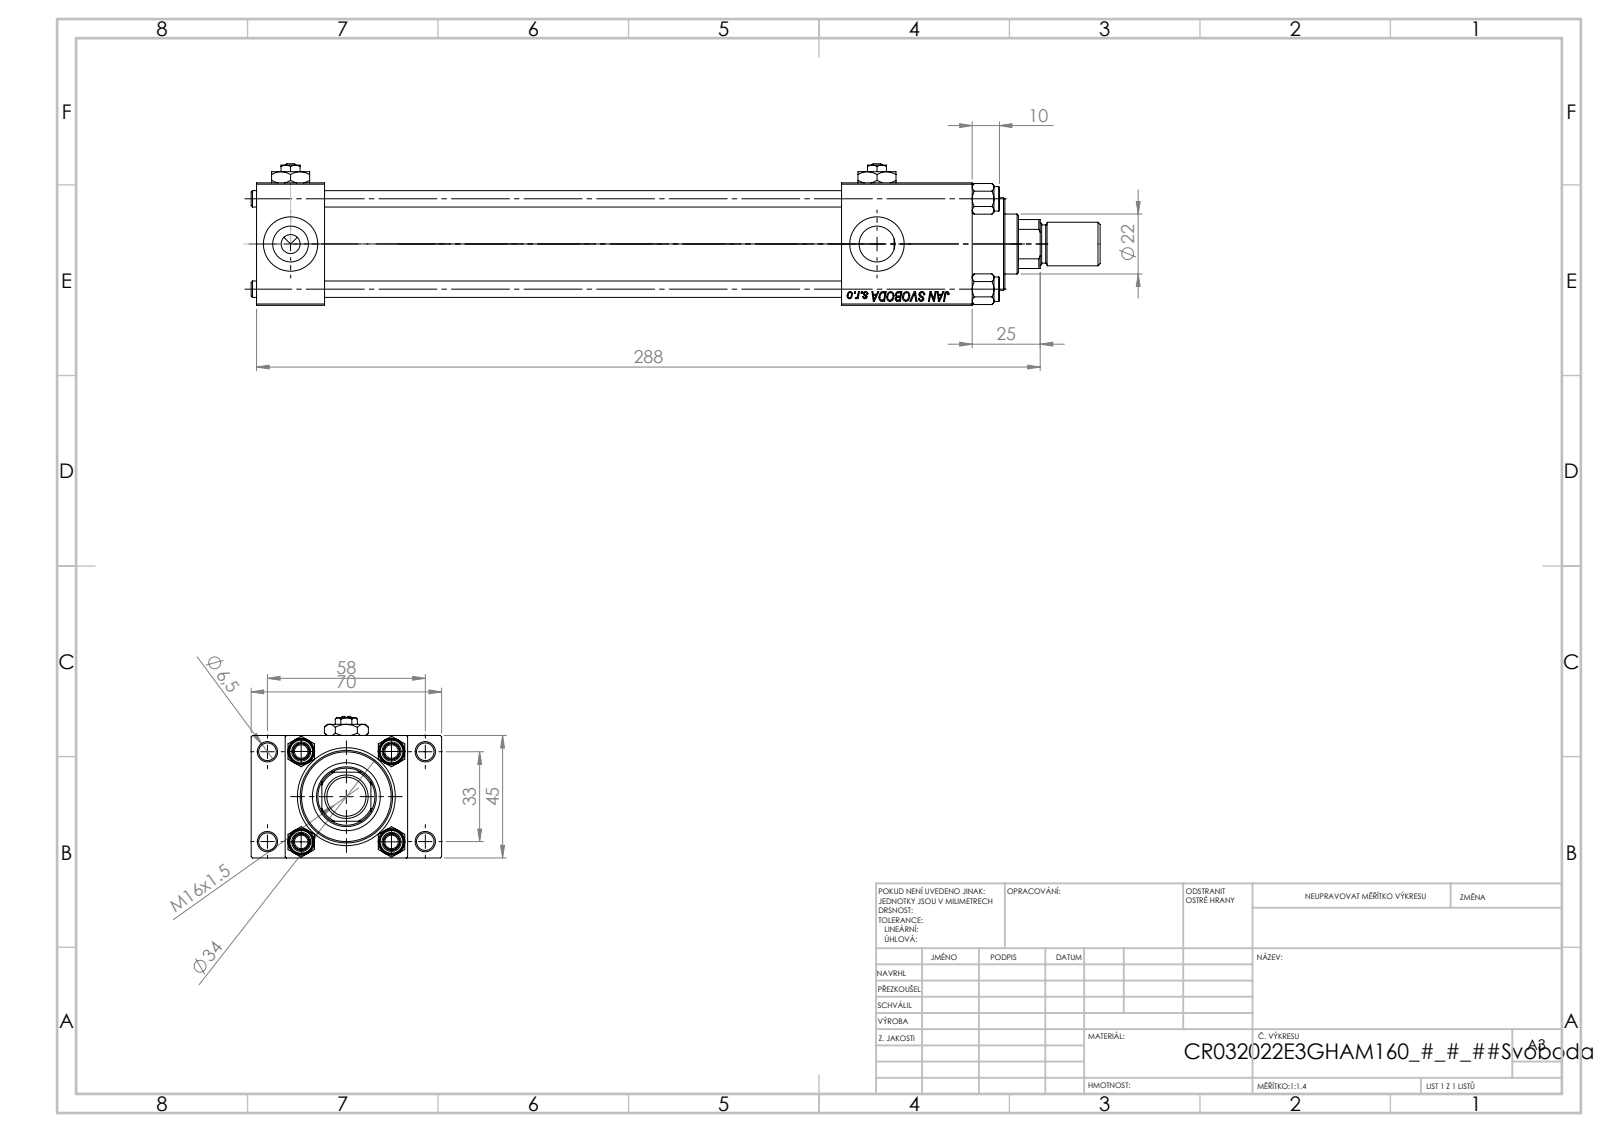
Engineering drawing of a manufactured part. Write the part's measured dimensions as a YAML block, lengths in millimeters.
part_name: "V215_VC_A; V215CR_E_Body; Zatka_pro_OIL_PORT; V215CR_VCP_E (+3 more)"
step_written_by: "SolidWorks 2019 (CONFIG_CONTROL_DESIGN)"
units: millimeters
bodies: {solids: 14, faces: 1249, planar: 548, cylindrical: 101, other: 600}
overall_size: [312, 70, 52]
volume: 353753
surface_area: 135327
round_holes:
  - {diameter: 6, count: 4}
  - {diameter: 6.5, count: 4}
  - {diameter: 13.16, count: 4}
  - {diameter: 20, count: 4}
  - {diameter: 7, count: 3}
  - {diameter: 10.5, count: 1}
  - {diameter: 22, count: 1}
  - {diameter: 24, count: 1}
  - {diameter: 25, count: 1}
  - {diameter: 32, count: 1}
  - {diameter: 33, count: 1}
round_bosses_or_shafts:
  - {diameter: 9, count: 4}
  - {diameter: 38, count: 1}
  - {diameter: 34, count: 1}
  - {diameter: 16, count: 1}
  - {diameter: 14, count: 1}
partial_cylinders:
  - {radius: 10.5, count: 1}
face_to_face_distances: [45, 25, 12.5, 57.5, 263, 215, 190, 238, 48, 234.3]
hole_center_spacings: [12.4, 23.48, 33.2, 33.37, 35.35, 45.6, 56.35, 33]
